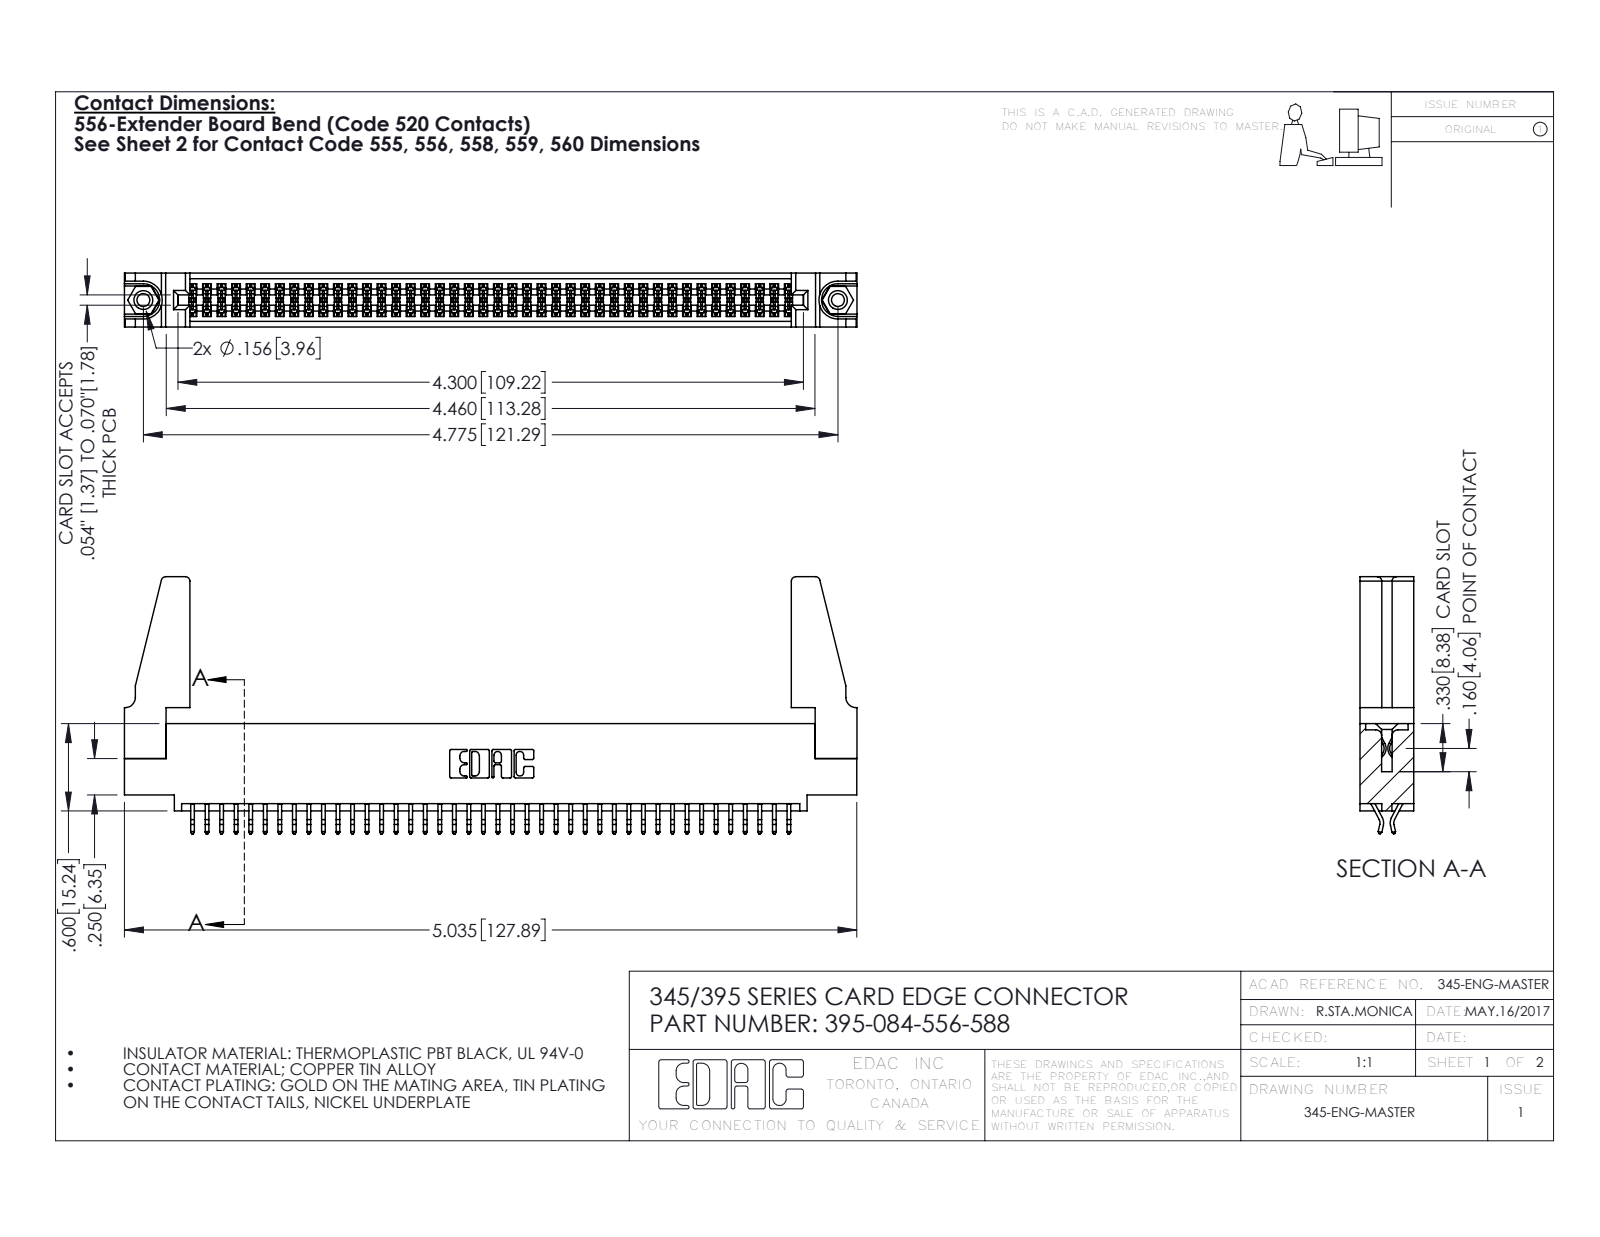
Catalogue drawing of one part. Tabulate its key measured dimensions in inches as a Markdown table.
| quantity | value |
| --- | --- |
| part name | 345-250-001_345-250-001-102; 345-220-078_345-220-088; 395-084-556-588; 345-292-001_556 Tail (+1 more) |
| STEP written by | SolidWorks 2016 (CONFIG_CONTROL_DESIGN) |
| units | inches |
| bodies | 89 solids, 4958 faces (3264 planar, 1678 cylindrical, 16 other) |
| overall size | 5.036 × 1.767 × 0.37 |
| volume | 0.952 in³ |
| surface area | 33.16 in² |
| round holes (diameter × count) | 0.089 × 2, 0.125 × 2, 0.156 × 2, 0.064 × 1 |
| round bosses / shafts (diameter × count) | 0.155 × 2 |
| partial cylindrical surfaces (radius × count) | 0.006 × 126, 0.01 × 22, 0.03 × 8, 0.007 × 6, 0.031 × 6, 0.026 × 3, 0.01 × 2, 0.014 × 2 |
| main face-to-face distances | 0.072, 0.298, 0.37, 0.025, 0.2, 0.098, 0.272, 0.225, 0.175, 0.149 |
| hole center spacings | 0.27, 4.539, 4.775 |
